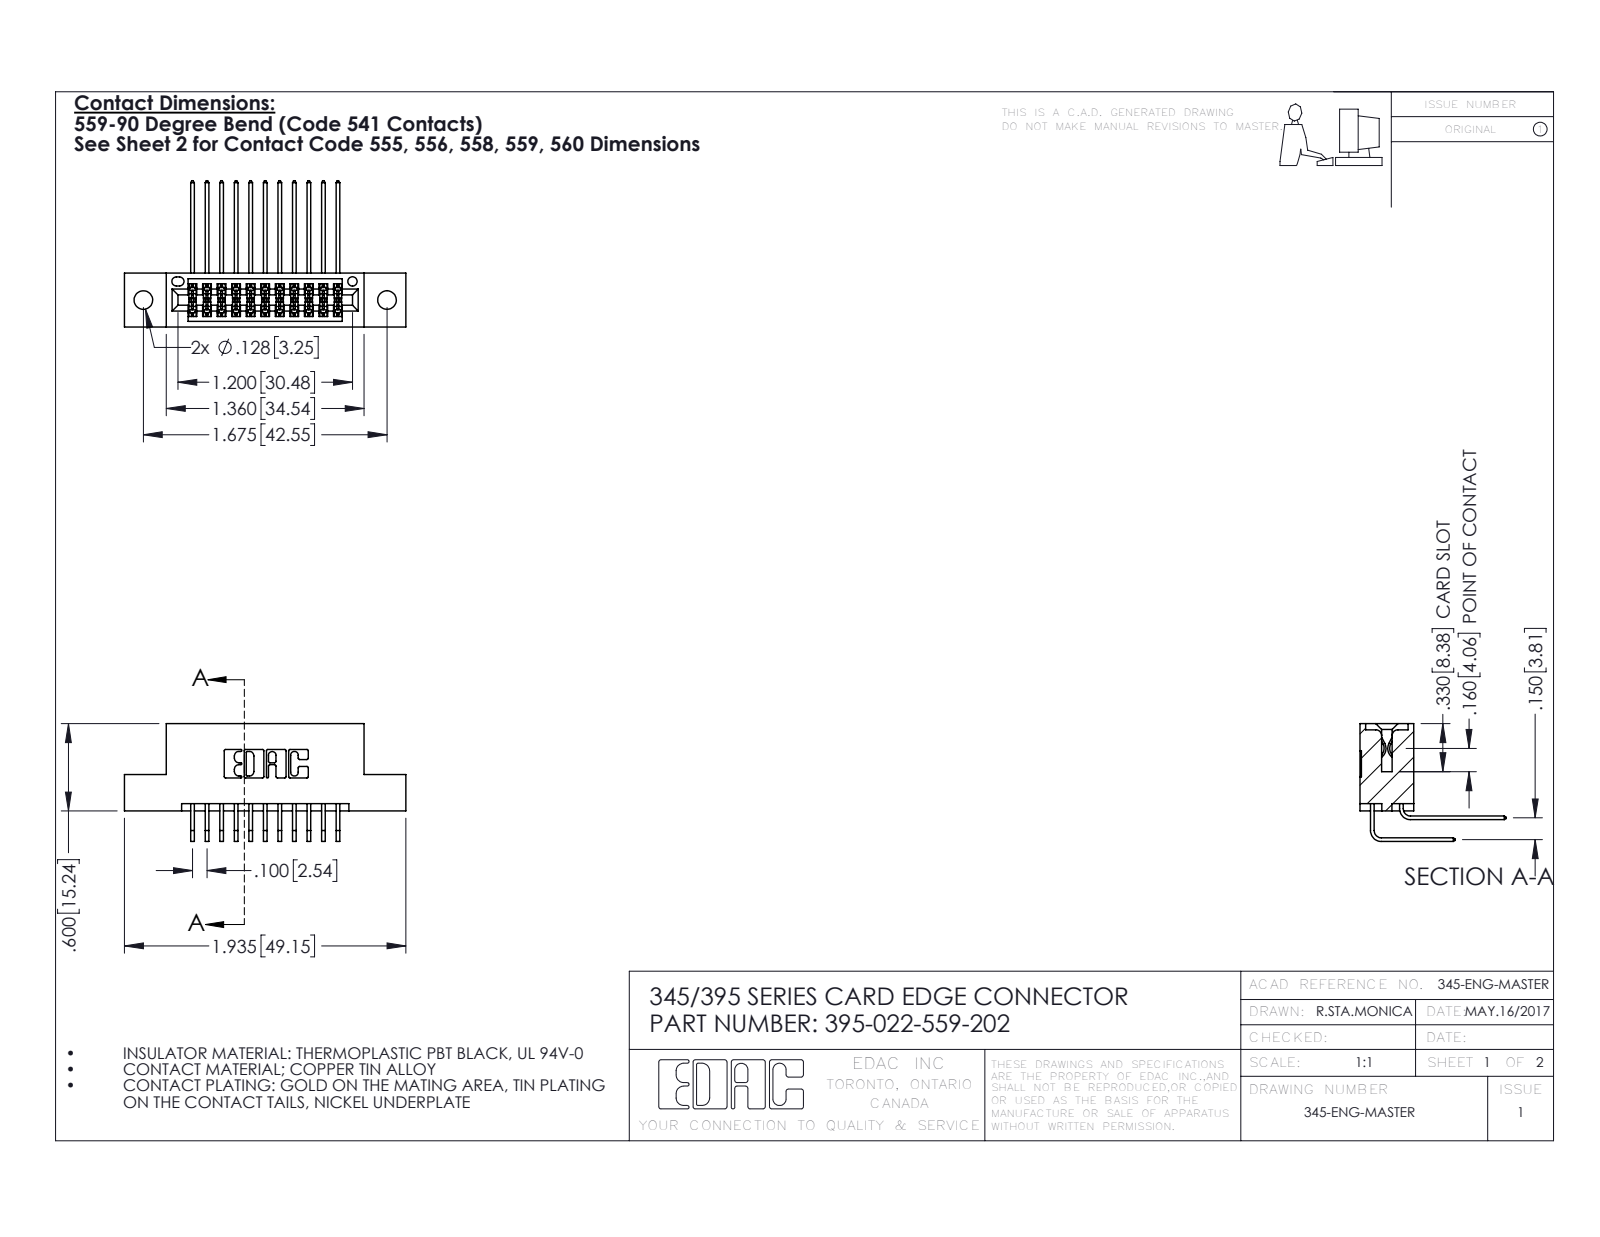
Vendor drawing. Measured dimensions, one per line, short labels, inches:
name: 345 Part_Flush Mounting Lugs - 0.128 Dia; 395-022-559-202; 345-292-001_558 559 Tail - 1; 345-292-001_559 Tail - 2
written by: SolidWorks 2016 (CONFIG_CONTROL_DESIGN)
unit: in
bodies: 23 solids, 1270 faces (850 planar, 420 cylindrical, 0 other)
size: 1.935 × 1.005 × 0.809
volume: 0.279 in³; area: 10.06 in²
holes: 2× ⌀0.128, 1× ⌀0.064
rounds: 34× R0.006, 22× R0.01, 6× R0.007, 6× R0.031, 3× R0.026, 2× R0.014, 2× R0.019, 2× R0.022
face distances: 0.2, 0.072, 0.298, 0.37, 0.098, 0.272, 0.025, 0.15, 0.225, 0.1
hole spacings: 0.27, 1.443, 1.675
